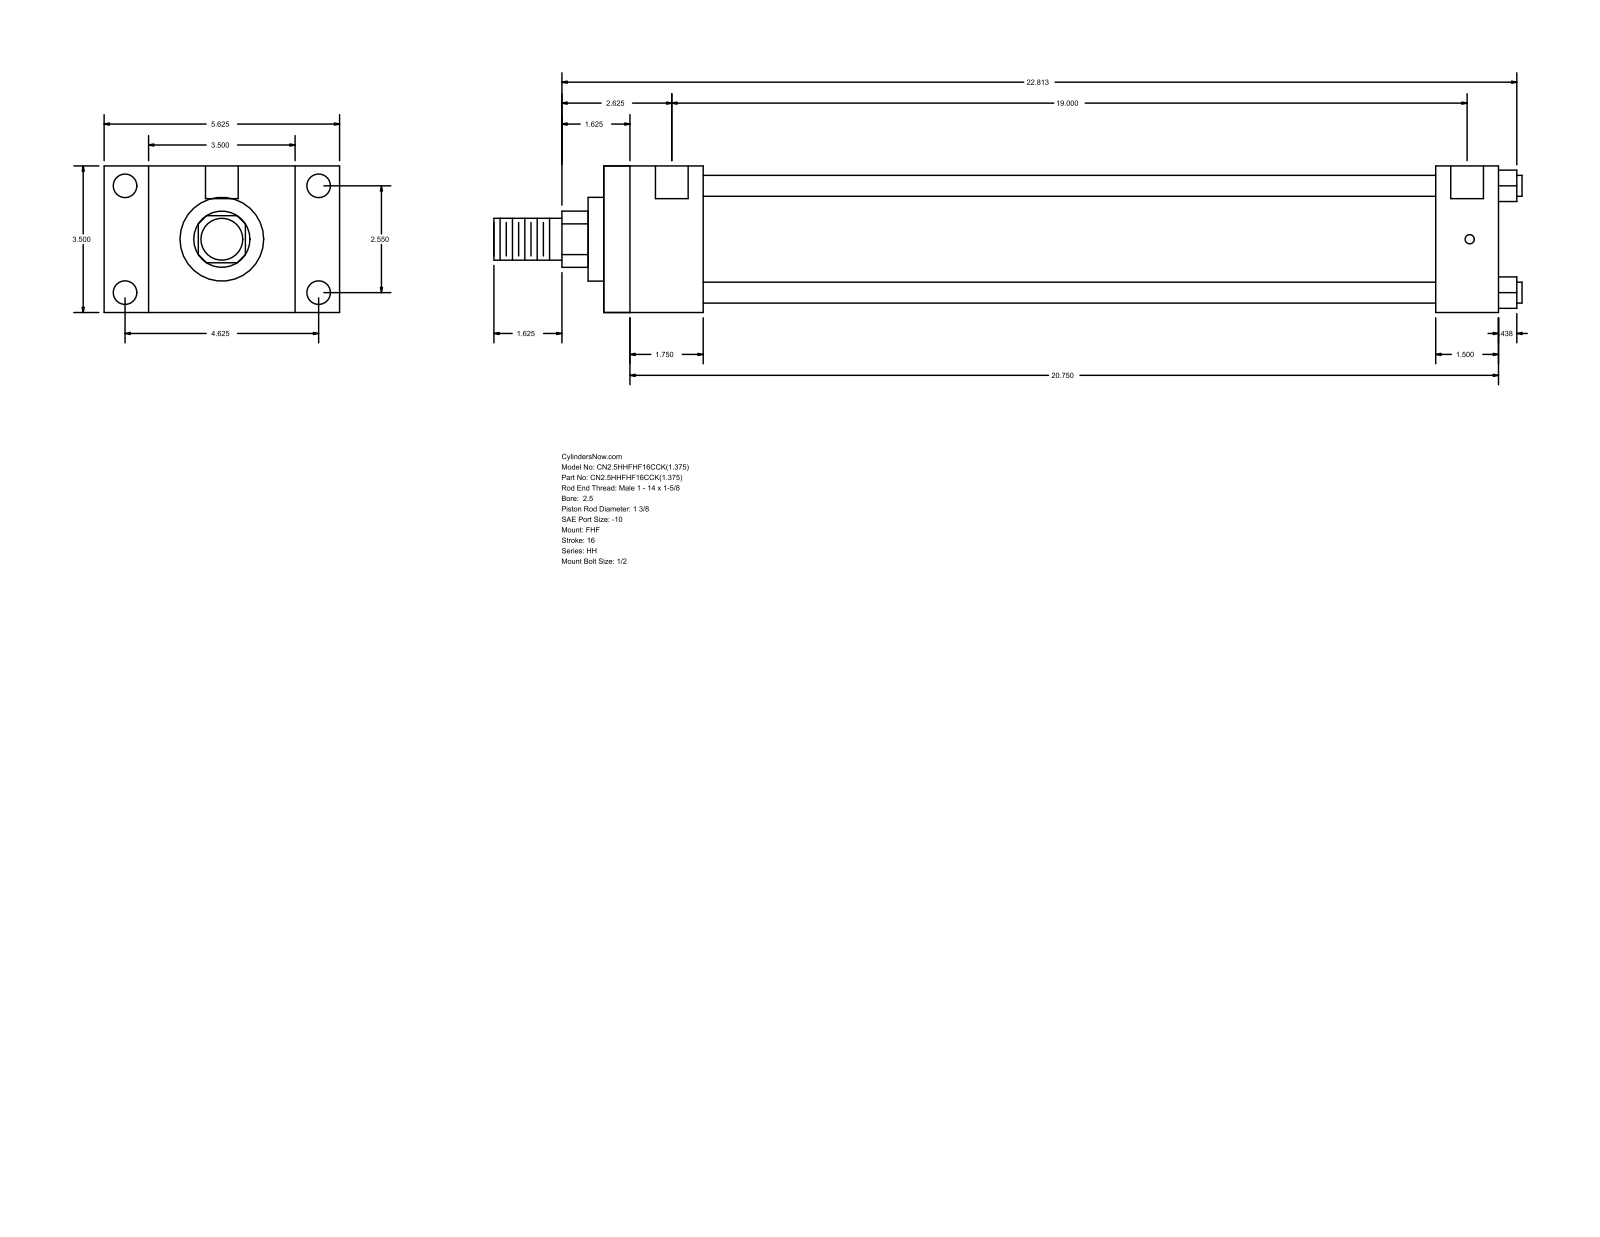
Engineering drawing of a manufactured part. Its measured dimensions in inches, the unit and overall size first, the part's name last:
Units: inches
Overall size (bounding box): 24.563 × 5.625 × 3.5
Round holes (diameter × count): ⌀0.219 ×4, ⌀0.563 ×4, ⌀0.781 ×2
Round bosses / shafts (diameter × count): ⌀0.5 ×4, ⌀2.875 ×1, ⌀2 ×1, ⌀1.375 ×1, ⌀1 ×1
Partial cylindrical surfaces — rounded edges, fillets, slot ends (radius × count): R0.672 ×1
Main face-to-face distances: 3.5, 2.375, 1.063, 4.563, 21.375, 19, 5.625, 19.875, 17.5, 1.5
Hole centre spacings: 2.55, 4.625, 5.281, 19.125, 0.062, 0.063, 19, 19.062
Bodies: 0 solids, 88 faces (60 planar, 28 cylindrical, 0 other)
Part name (STEP PRODUCT): HH_FHF__0250_1.375
STEP written by: GSSL Pune (CONFIG_CONTROL_DESIGN)
